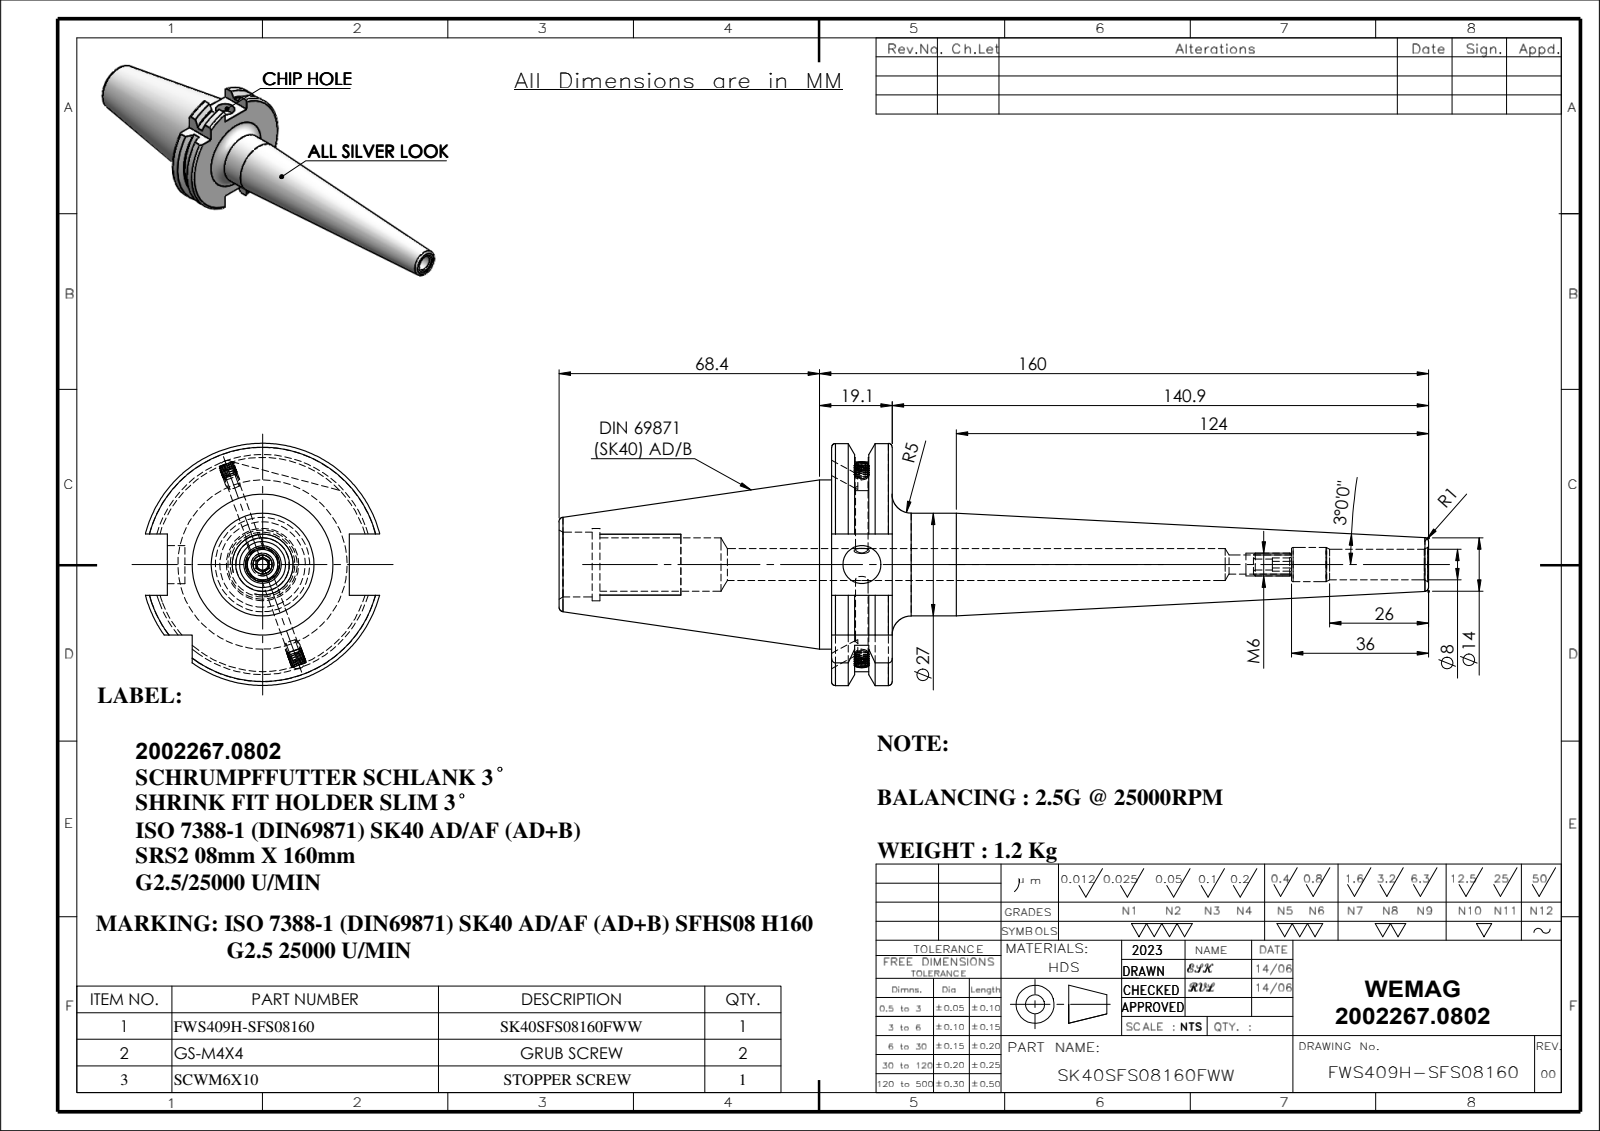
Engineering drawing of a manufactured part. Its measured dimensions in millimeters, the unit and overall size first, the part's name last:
Units: millimetres
Overall size (bounding box): 228.4 × 63.55 × 61.48
Round holes (diameter × count): ⌀2.9 ×1, ⌀3.3 ×1, ⌀5 ×1, ⌀8 ×1, ⌀8.4 ×1, ⌀9 ×1, ⌀10 ×1, ⌀14 ×1, ⌀17 ×1, ⌀19 ×1
Round bosses / shafts (diameter × count): ⌀4 ×2, ⌀44.45 ×1, ⌀27 ×1, ⌀6 ×1
Partial cylindrical surfaces — rounded edges, fillets, slot ends (radius × count): R28.12 ×1, R31.77 ×1
Main face-to-face distances: 15.9, 16.1, 47.8, 71.6, 87.5, 10.7, 60.9, 76.8, 77.62, 66.92
Volume: 148 185 mm³ · Surface area: 33 609 mm²
Bodies: 4 solids, 230 faces (62 planar, 60 cylindrical, 108 other)
Part name (STEP PRODUCT): SK40SFS08160FWW; GS-M4X4_DIN 913 - M4 x 4-N; 91406-SRS208160; SCWM6-10
STEP written by: SolidWorks 2018 (CONFIG_CONTROL_DESIGN)
